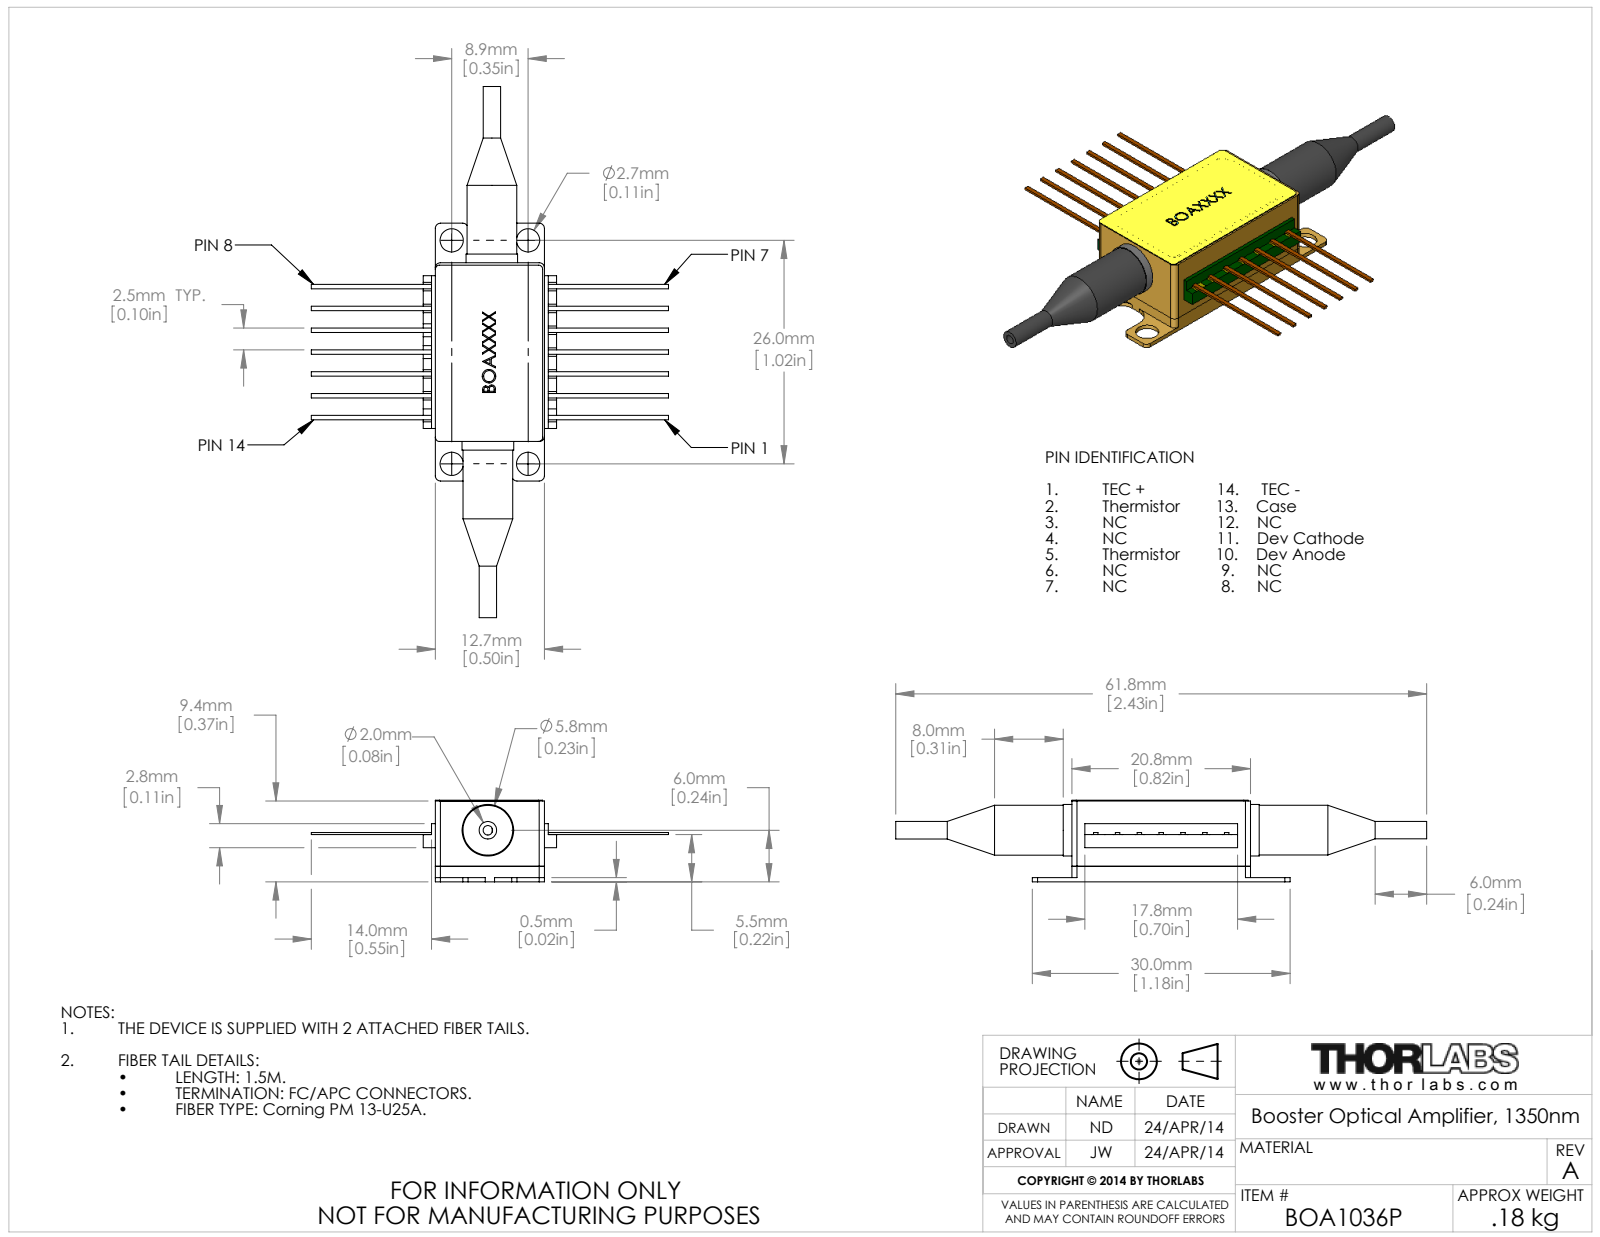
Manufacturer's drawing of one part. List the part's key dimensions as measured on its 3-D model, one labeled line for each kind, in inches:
Part name (STEP PRODUCT): QTN007639-E0W
STEP written by: SolidWorks 2012 (AUTOMOTIVE_DESIGN)
Units: inches
Bodies: 0 solids, 267 faces (201 planar, 48 cylindrical, 18 other)
Overall size (bounding box): 2.433 × 1.638 × 0.374
Round holes (diameter × count): ⌀0.106 ×4, ⌀0.043 ×2
Round bosses / shafts (diameter × count): ⌀0.236 ×2, ⌀0.228 ×2, ⌀0.08 ×2
Partial cylindrical surfaces — rounded edges, fillets, slot ends (radius × count): R0.024 ×12, R0.02 ×4, R0.079 ×4
Main face-to-face distances: 0.374, 0.5, 0.156, 0.218, 0.217, 0.06, 0.158, 0.02, 0.226, 0.07
Hole centre spacings: 0.35, 1.024, 1.082, 0.019
